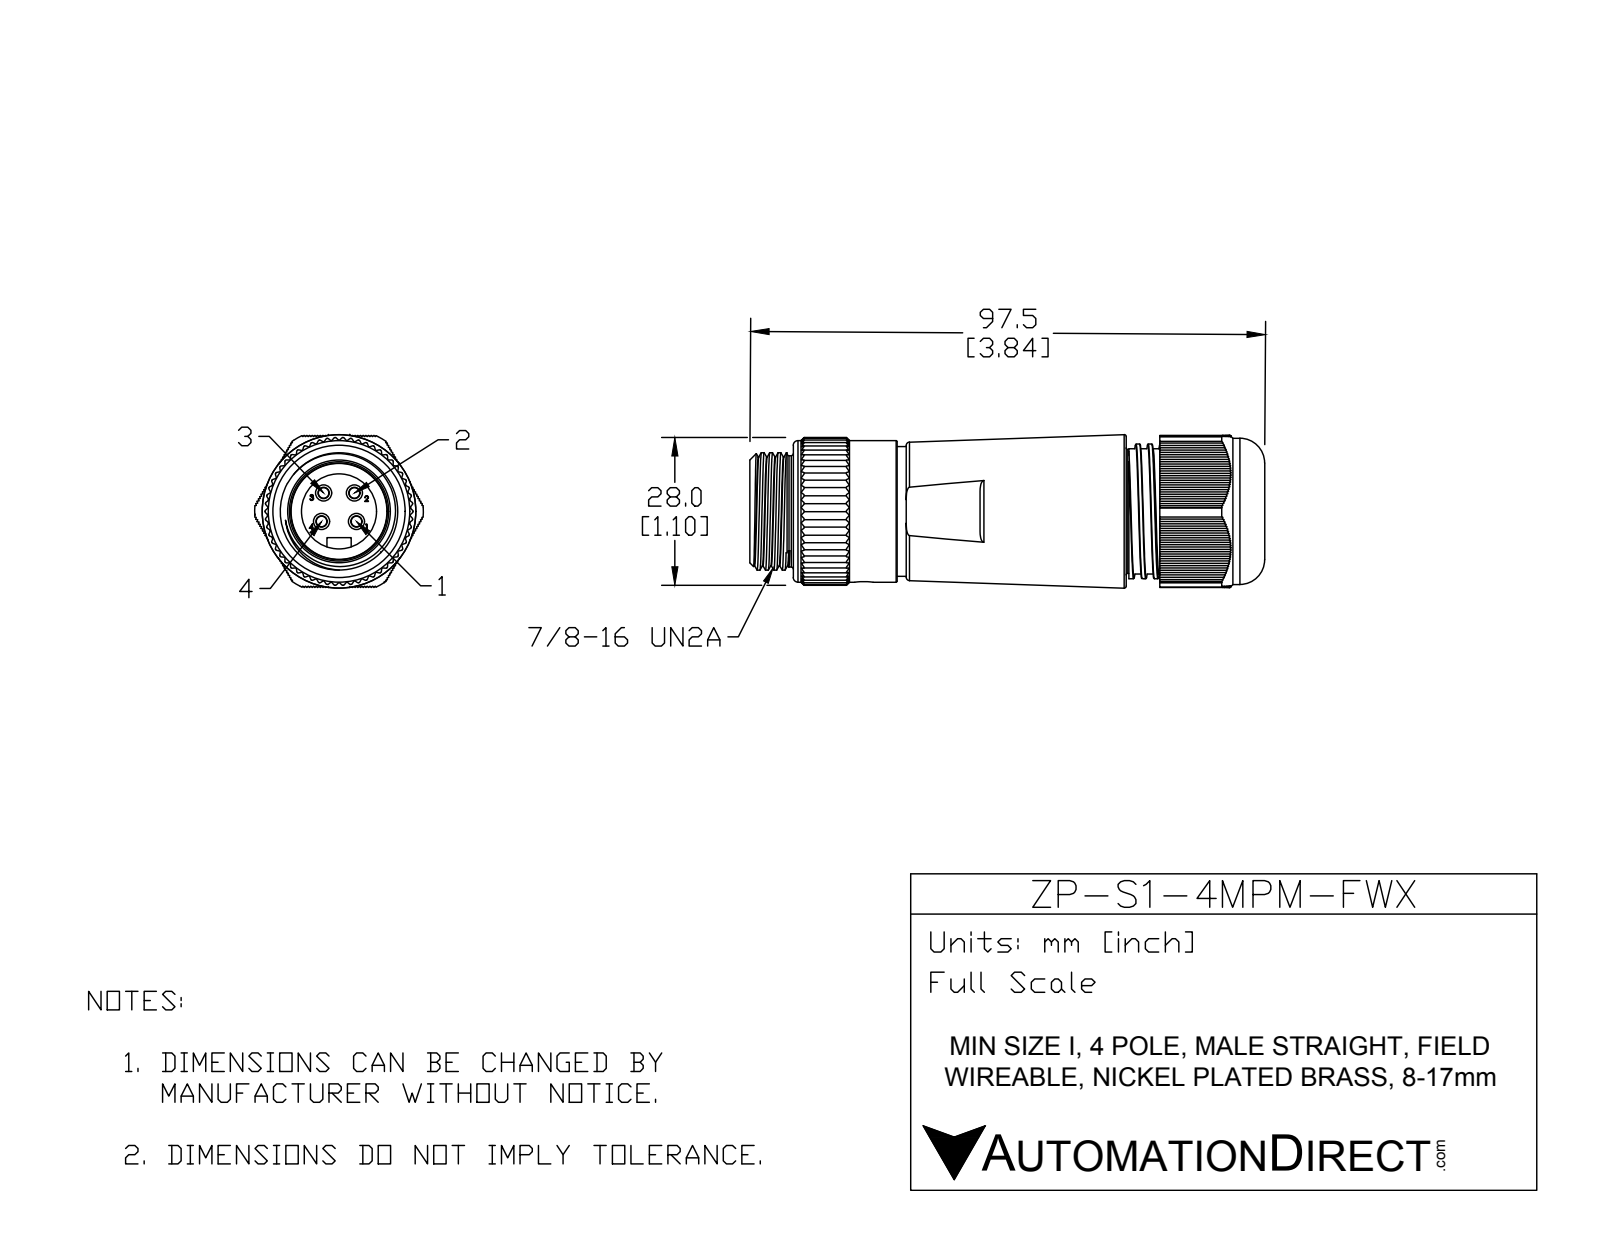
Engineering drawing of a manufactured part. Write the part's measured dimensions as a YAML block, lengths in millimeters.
part_name: "MIN-4MPM-FWX"
step_written_by: "SolidWorks 2015 (AUTOMOTIVE_DESIGN)"
units: millimeters
bodies: {solids: 1, faces: 1122, planar: 689, cylindrical: 350, other: 83}
overall_size: [97.49, 31.9, 29.06]
volume: 53506
surface_area: 16353
round_holes:
  - {diameter: 3.5, count: 1}
  - {diameter: 14.22, count: 1}
  - {diameter: 17.27, count: 1}
  - {diameter: 18.29, count: 1}
  - {diameter: 24.13, count: 1}
  - {diameter: 25.4, count: 1}
round_bosses_or_shafts:
  - {diameter: 3.05, count: 4}
  - {diameter: 2, count: 4}
  - {diameter: 27.69, count: 1}
  - {diameter: 26.8, count: 1}
  - {diameter: 25.5, count: 1}
  - {diameter: 24.56, count: 1}
  - {diameter: 24, count: 1}
  - {diameter: 22.23, count: 1}
partial_cylinders:
  - {radius: 0.25, count: 116}
  - {radius: 0.2, count: 58}
  - {radius: 2.29, count: 1}
  - {radius: 14, count: 1}
  - {radius: 15.95, count: 1}
face_to_face_distances: [0.36, 0.72, 1.08, 6.35, 18.11, 69.78, 1.44, 19.16, 24.46, 1.8]
